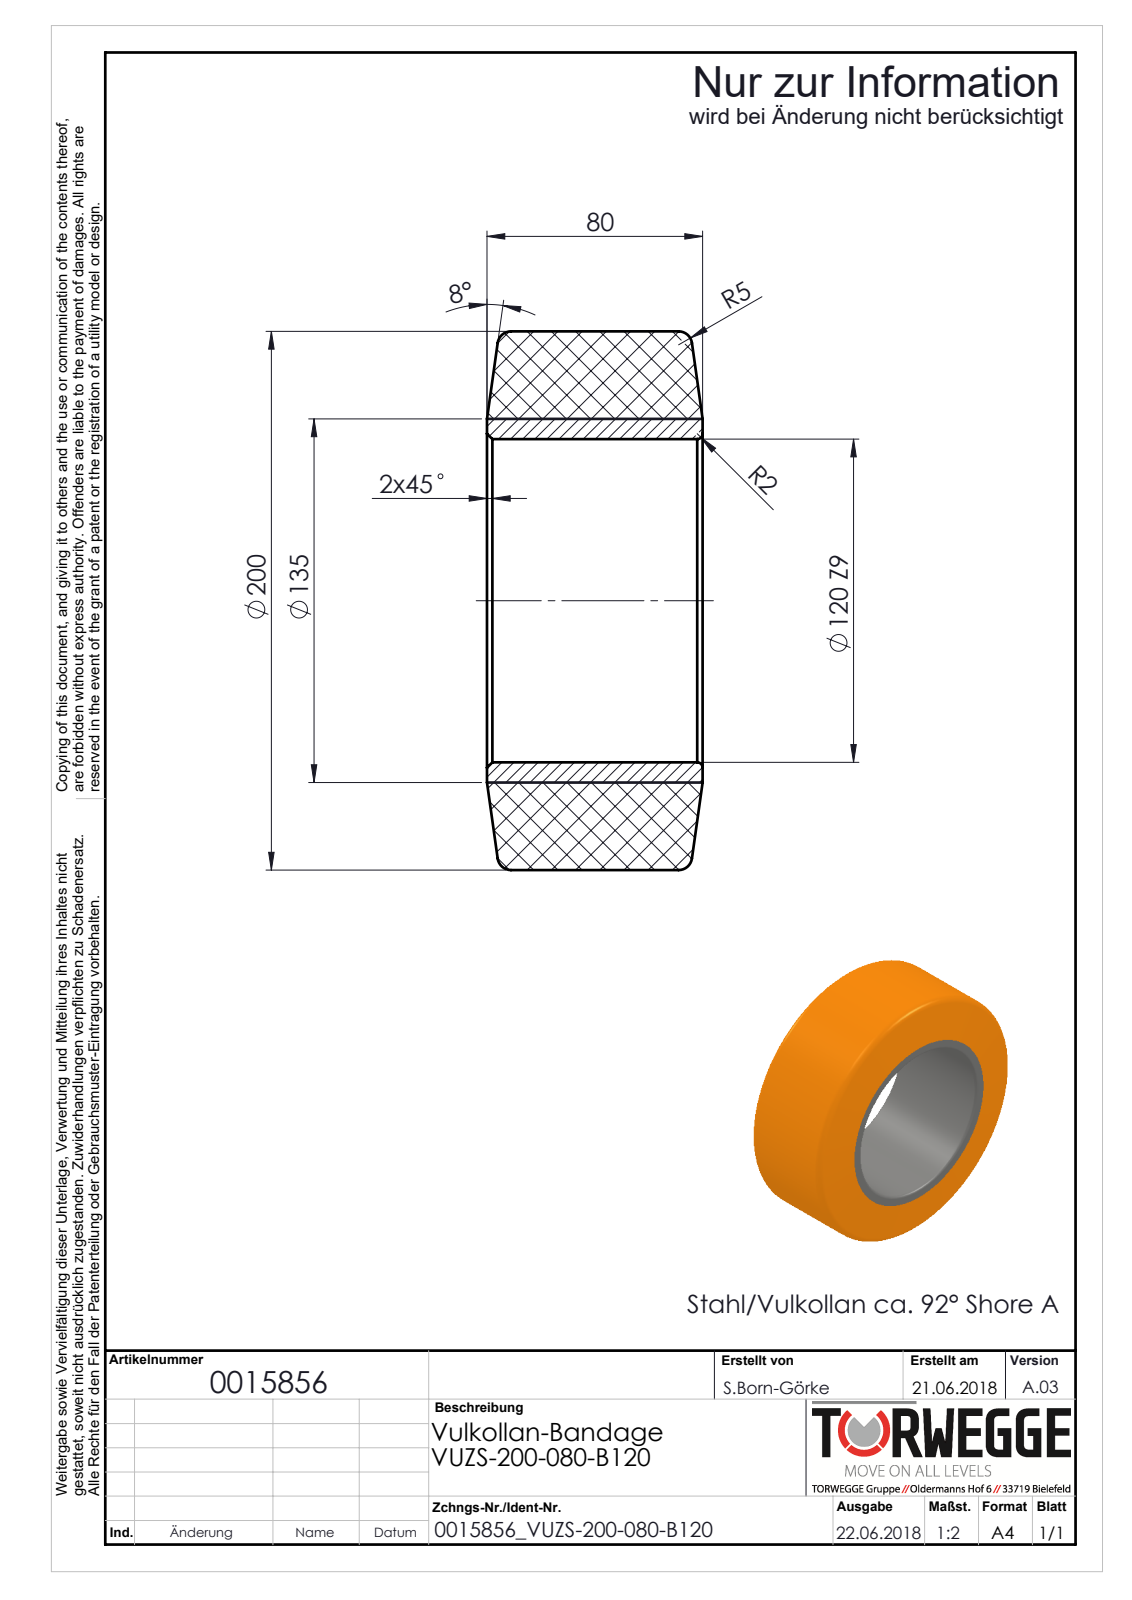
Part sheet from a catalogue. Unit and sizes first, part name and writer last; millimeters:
Units: millimetres
Overall size (bounding box): 200 × 200 × 80
Round holes (diameter × count): ⌀120 ×1
Round bosses / shafts (diameter × count): ⌀200 ×1
Main face-to-face distances: 80
Volume: 1 519 000 mm³ · Surface area: 112 514 mm²
Bodies: 1 solid, 18 faces (2 planar, 4 cylindrical, 12 other)
Part name (STEP PRODUCT): 0015856_VUZS-200-080-B120
STEP written by: SolidWorks 2018 (AUTOMOTIVE_DESIGN)
